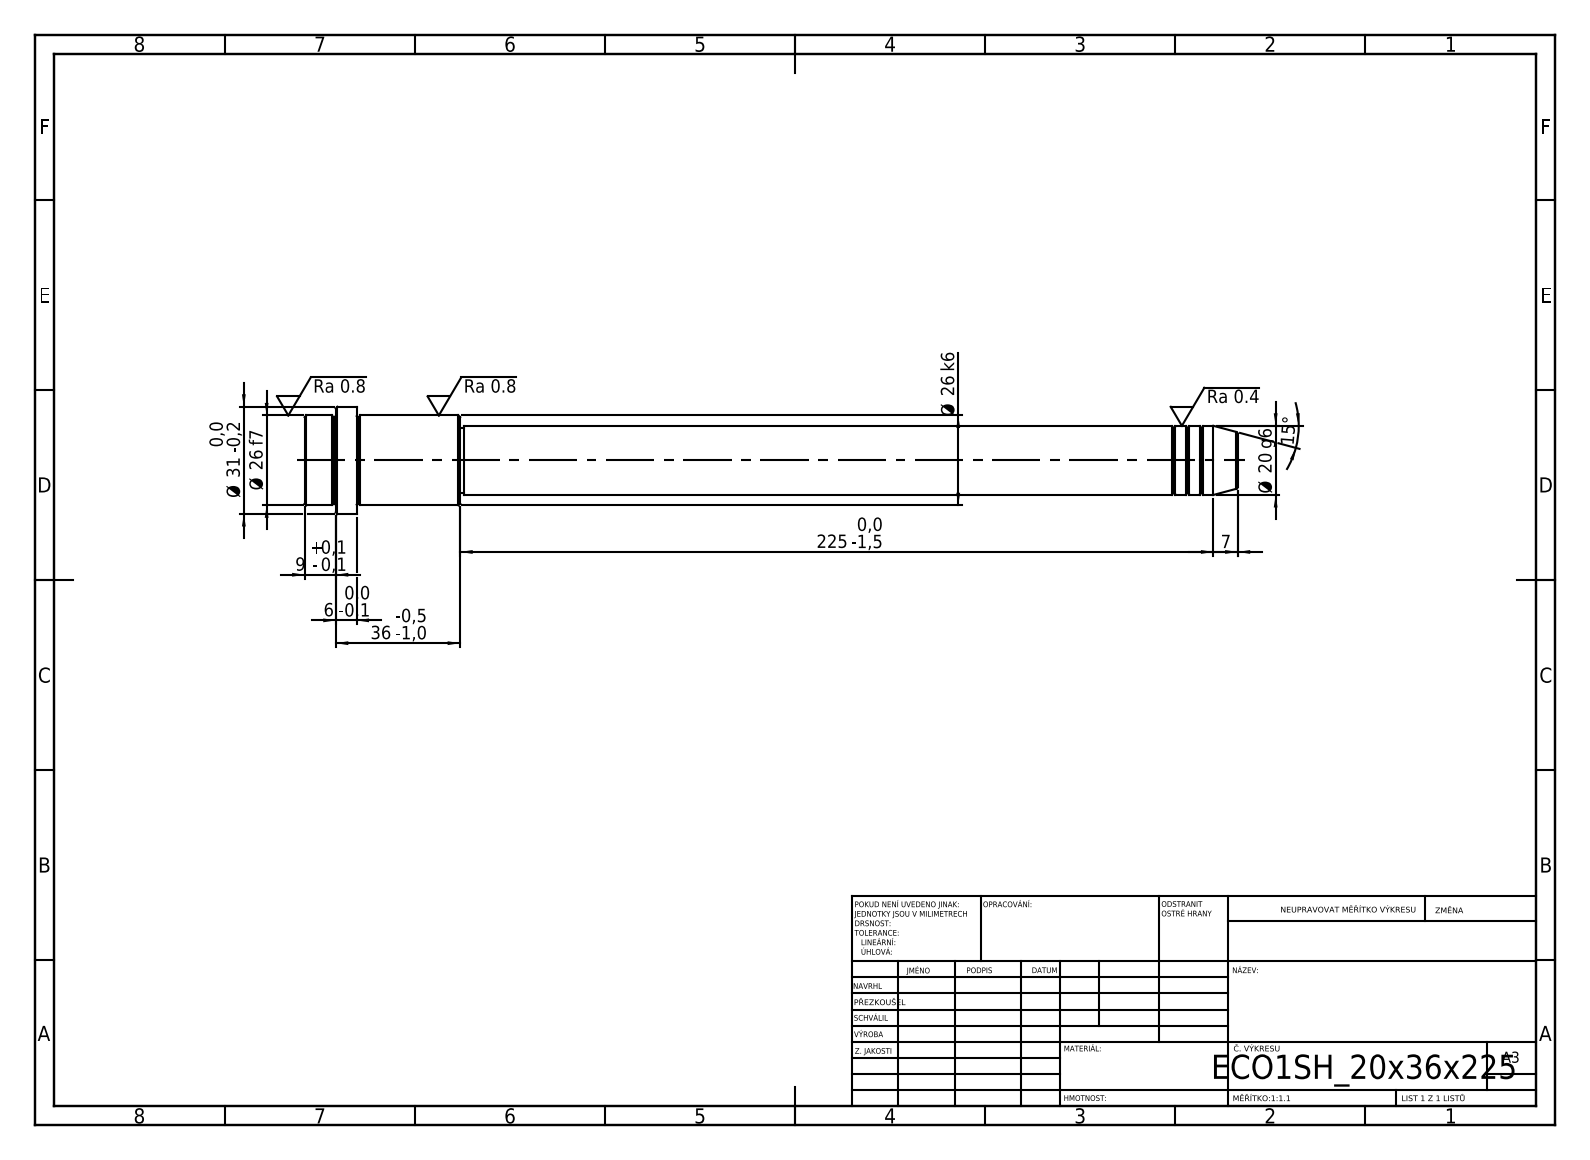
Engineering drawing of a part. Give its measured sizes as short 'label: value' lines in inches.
written by: SolidWorks 2019 (CONFIG_CONTROL_DESIGN)
unit: in
bodies: 1 solid, 52 faces (6 planar, 16 cylindrical, 30 other)
size: 10.63 × 1.22 × 1.22
volume: 5.818 in³; area: 30.14 in²
bosses: 1× ⌀1.22, 1× ⌀1.024, 1× ⌀0.787, 1× ⌀0.748
face distances: 0.591, 1.181, 1.772, 8.858, 10.039, 10.63, 10.276, 1.417, 0.236, 0.354
